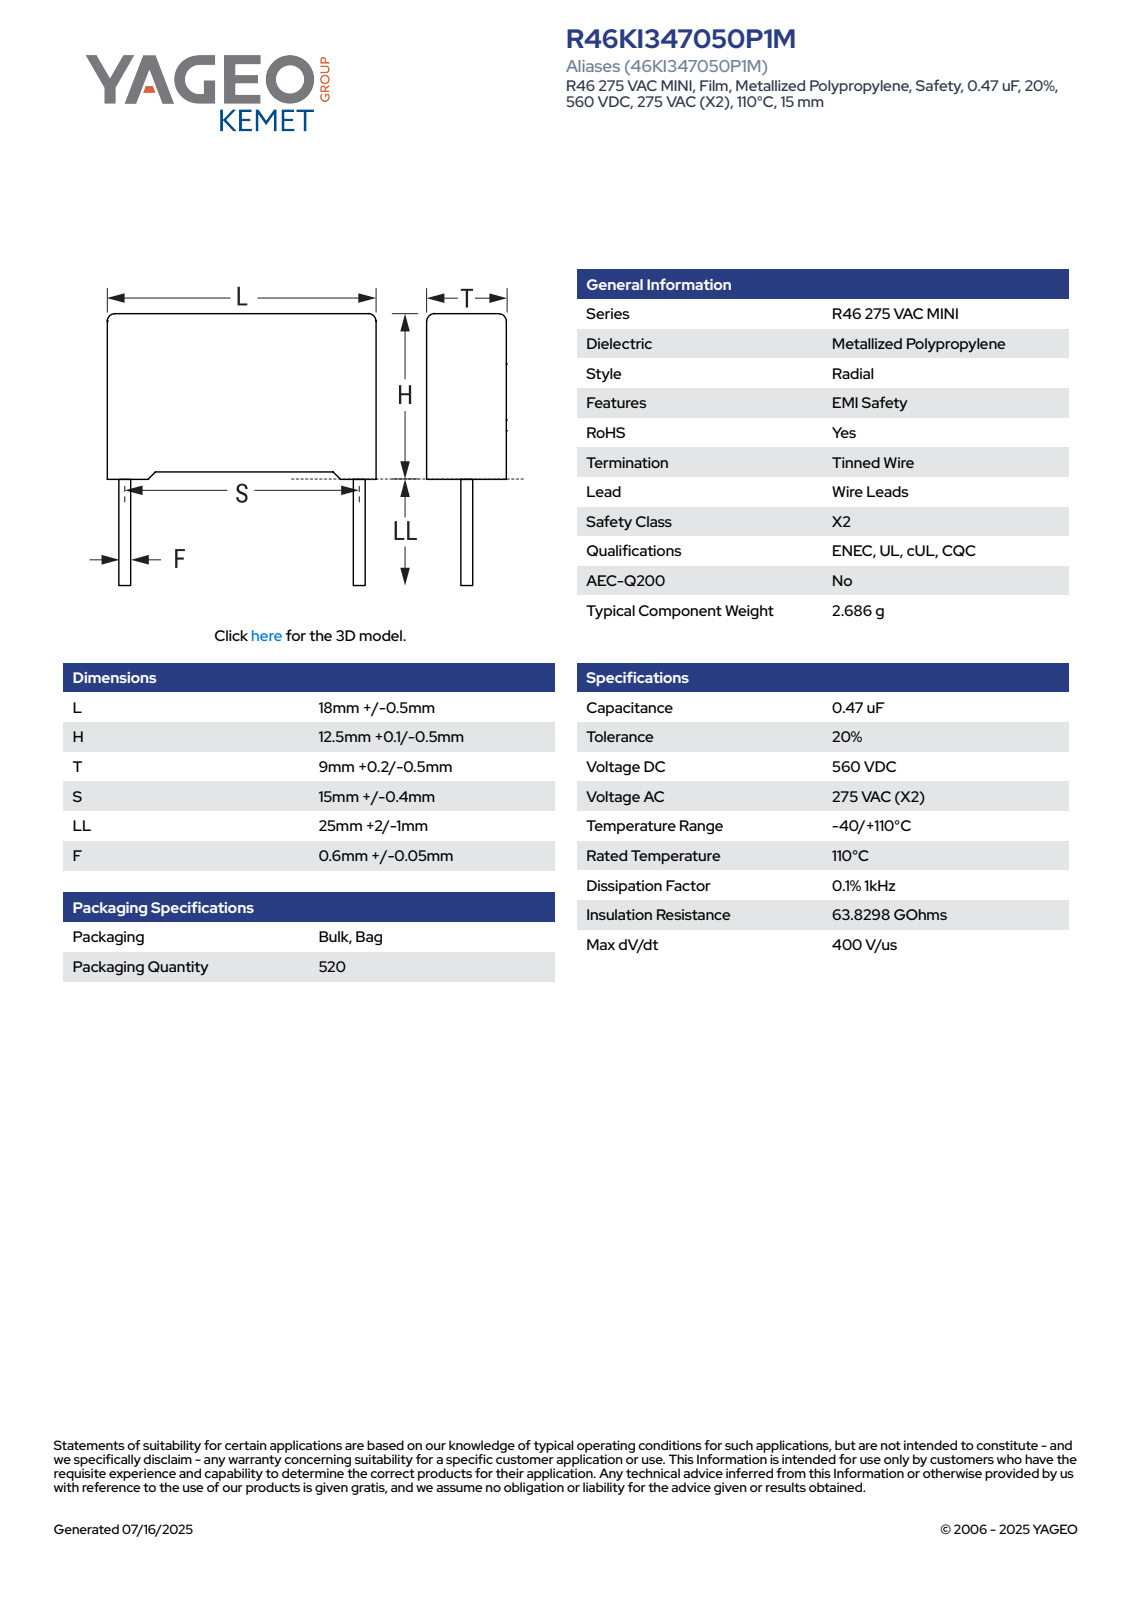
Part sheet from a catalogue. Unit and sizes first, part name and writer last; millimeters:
Units: millimetres
Overall size (bounding box): 39.6 × 18.5 × 9.21
Round bosses / shafts (diameter × count): ⌀0.65 ×2
Partial cylindrical surfaces — rounded edges, fillets, slot ends (radius × count): R0.5 ×4
Main face-to-face distances: 9.2, 11.85, 18.5, 0.62, 0.75, 12.6, 8.58, 0.43, 0.32, 12.17
Volume: 2 051 mm³ · Surface area: 1 184 mm²
Bodies: 4 solids, 85 faces (77 planar, 8 cylindrical, 0 other)
Part name (STEP PRODUCT): CFR_RB2_18X12.5X9_L18.5H12.6T9.2S15LL27F0.65
STEP written by: SolidWorks 2021 (AUTOMOTIVE_DESIGN)
